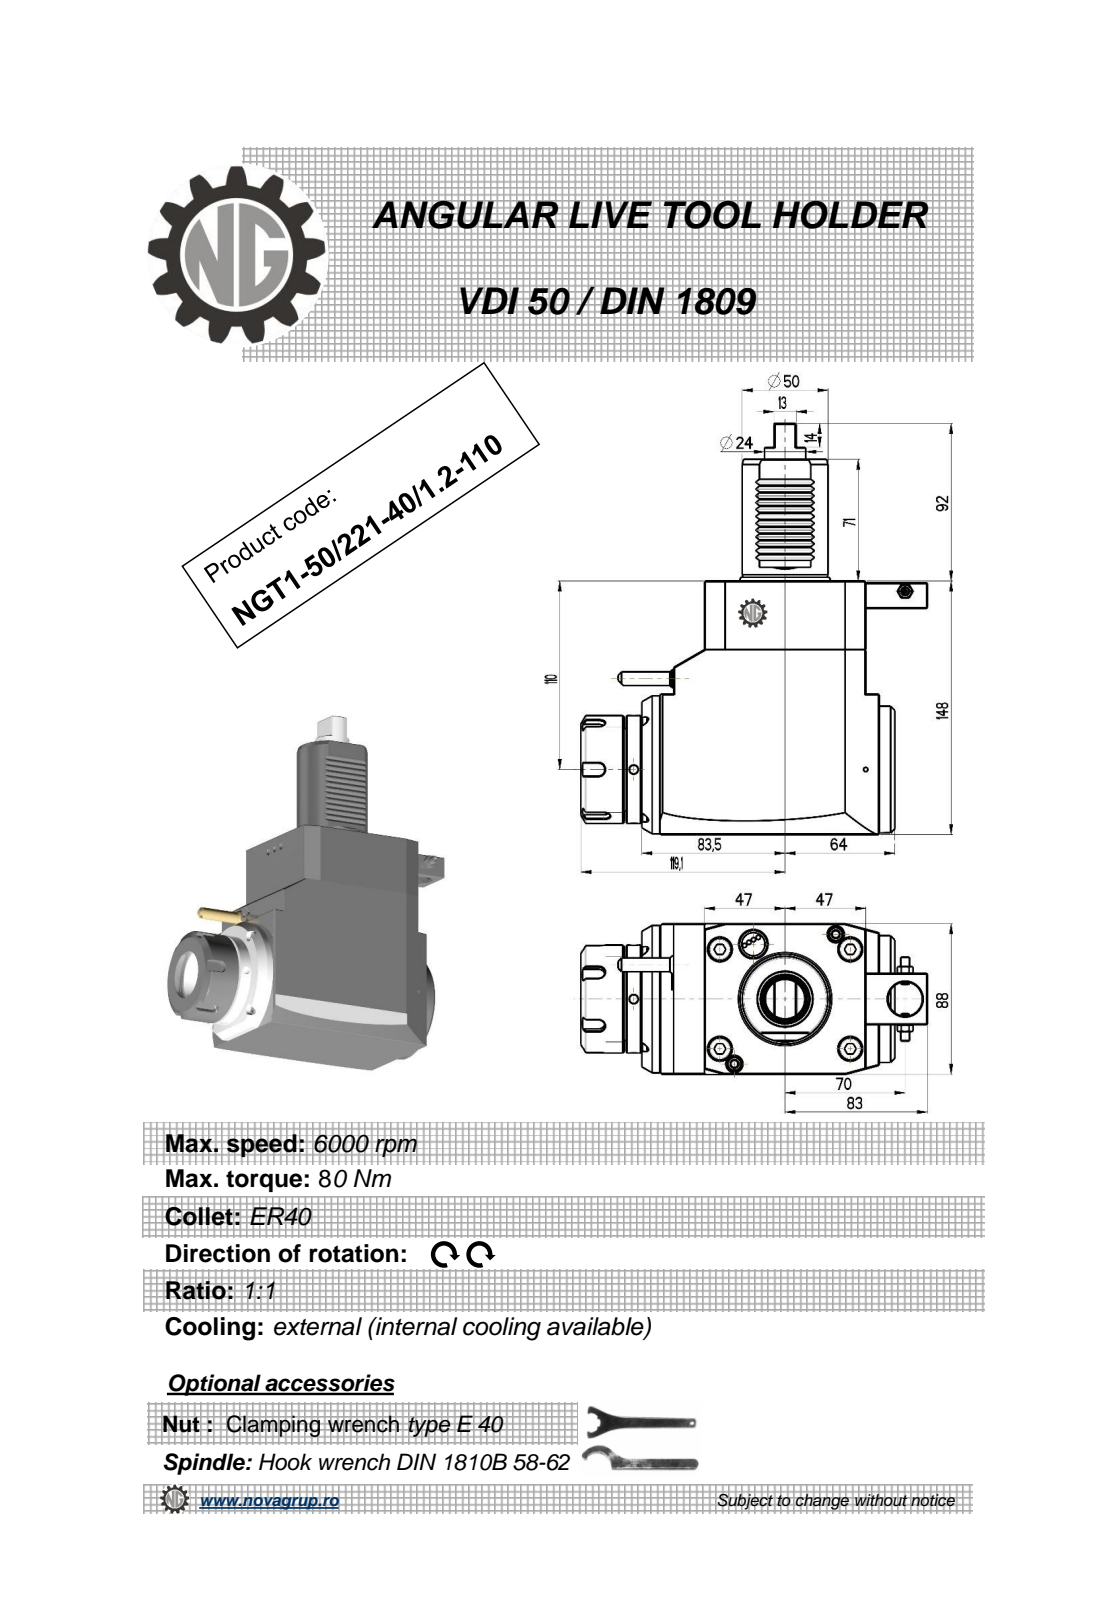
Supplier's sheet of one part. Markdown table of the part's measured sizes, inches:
| quantity | value |
| --- | --- |
| part name | NGT1_50_221_40_1_2_110 |
| STEP written by | PRO/ENGINEER BY PARAMETRIC TECHNOLOGY CORPORATION, 2010280 (CONFIG_CONTROL_DESIGN) |
| units | inches |
| bodies | 1 solid, 418 faces (207 planar, 95 cylindrical, 116 other) |
| overall size | 9.449 × 7.957 × 3.465 |
| volume | 111.8 in³ |
| surface area | 177.8 in² |
| round holes (diameter × count) | 0.197 × 3, 0.118 × 1, 0.177 × 1, 0.374 × 1, 0.787 × 1, 1.319 × 1 |
| round bosses / shafts (diameter × count) | 3.386 × 1, 2.913 × 1, 2.48 × 1, 2.008 × 1, 1.969 × 1, 0.945 × 1, 0.394 × 1, 0.353 × 1 |
| partial cylindrical surfaces (radius × count) | 0.01 × 12, 0.012 × 12, 0.008 × 6, 0.148 × 5, 0.031 × 2, 0.098 × 1 |
| main face-to-face distances | 3.465, 5.827, 5.807, 0.669, 0.315, 3.701, 4.37, 0.354, 1.437, 5.138 |
| hole center spacings | 2.065, 2.23, 3.996, 6.23 |
